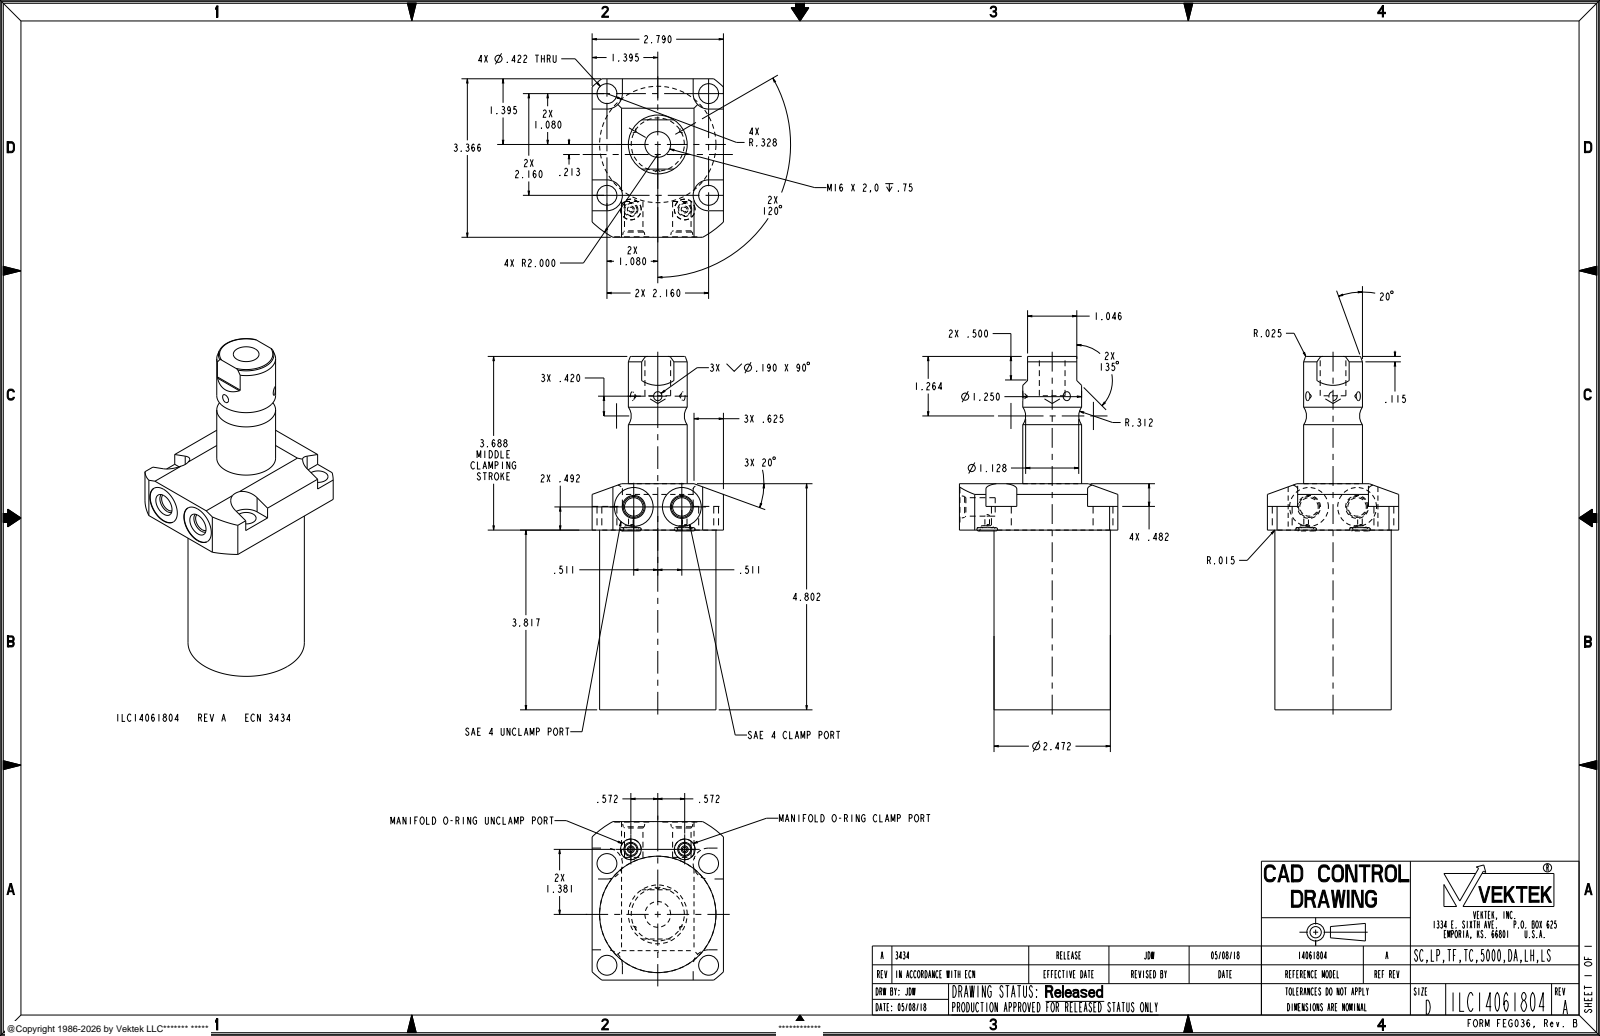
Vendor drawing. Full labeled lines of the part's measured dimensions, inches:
Part name (STEP PRODUCT): ILC14061804
STEP written by: PRO/ENGINEER BY PARAMETRIC TECHNOLOGY CORPORATION, 2013320 (AUTOMOTIVE_DESIGN)
Units: inches
Bodies: 3 solids, 119 faces (37 planar, 46 cylindrical, 36 other)
Overall size (bounding box): 7.505 × 3.366 × 2.79
Volume: 28.8 in³ · Surface area: 74.93 in²
Round holes (diameter × count): ⌀0.422 ×4, ⌀0.098 ×2, ⌀0.256 ×2, ⌀0.392 ×2, ⌀0.438 ×2, ⌀0.825 ×2, ⌀0.546 ×1
Round bosses / shafts (diameter × count): ⌀2.472 ×1, ⌀1.25 ×1
Partial cylindrical surfaces — rounded edges, fillets, slot ends (radius × count): R0.328 ×4, R0.03 ×2, R2 ×1
Main face-to-face distances: 3.817, 4.802, 0.985, 2.79, 4.32, 0.503, 0.482, 3.366, 7.505, 3.688
Hole centre spacings: 1.527, 2.16, 0.591, 1.495, 1.679, 2.513, 2.964, 3.054
